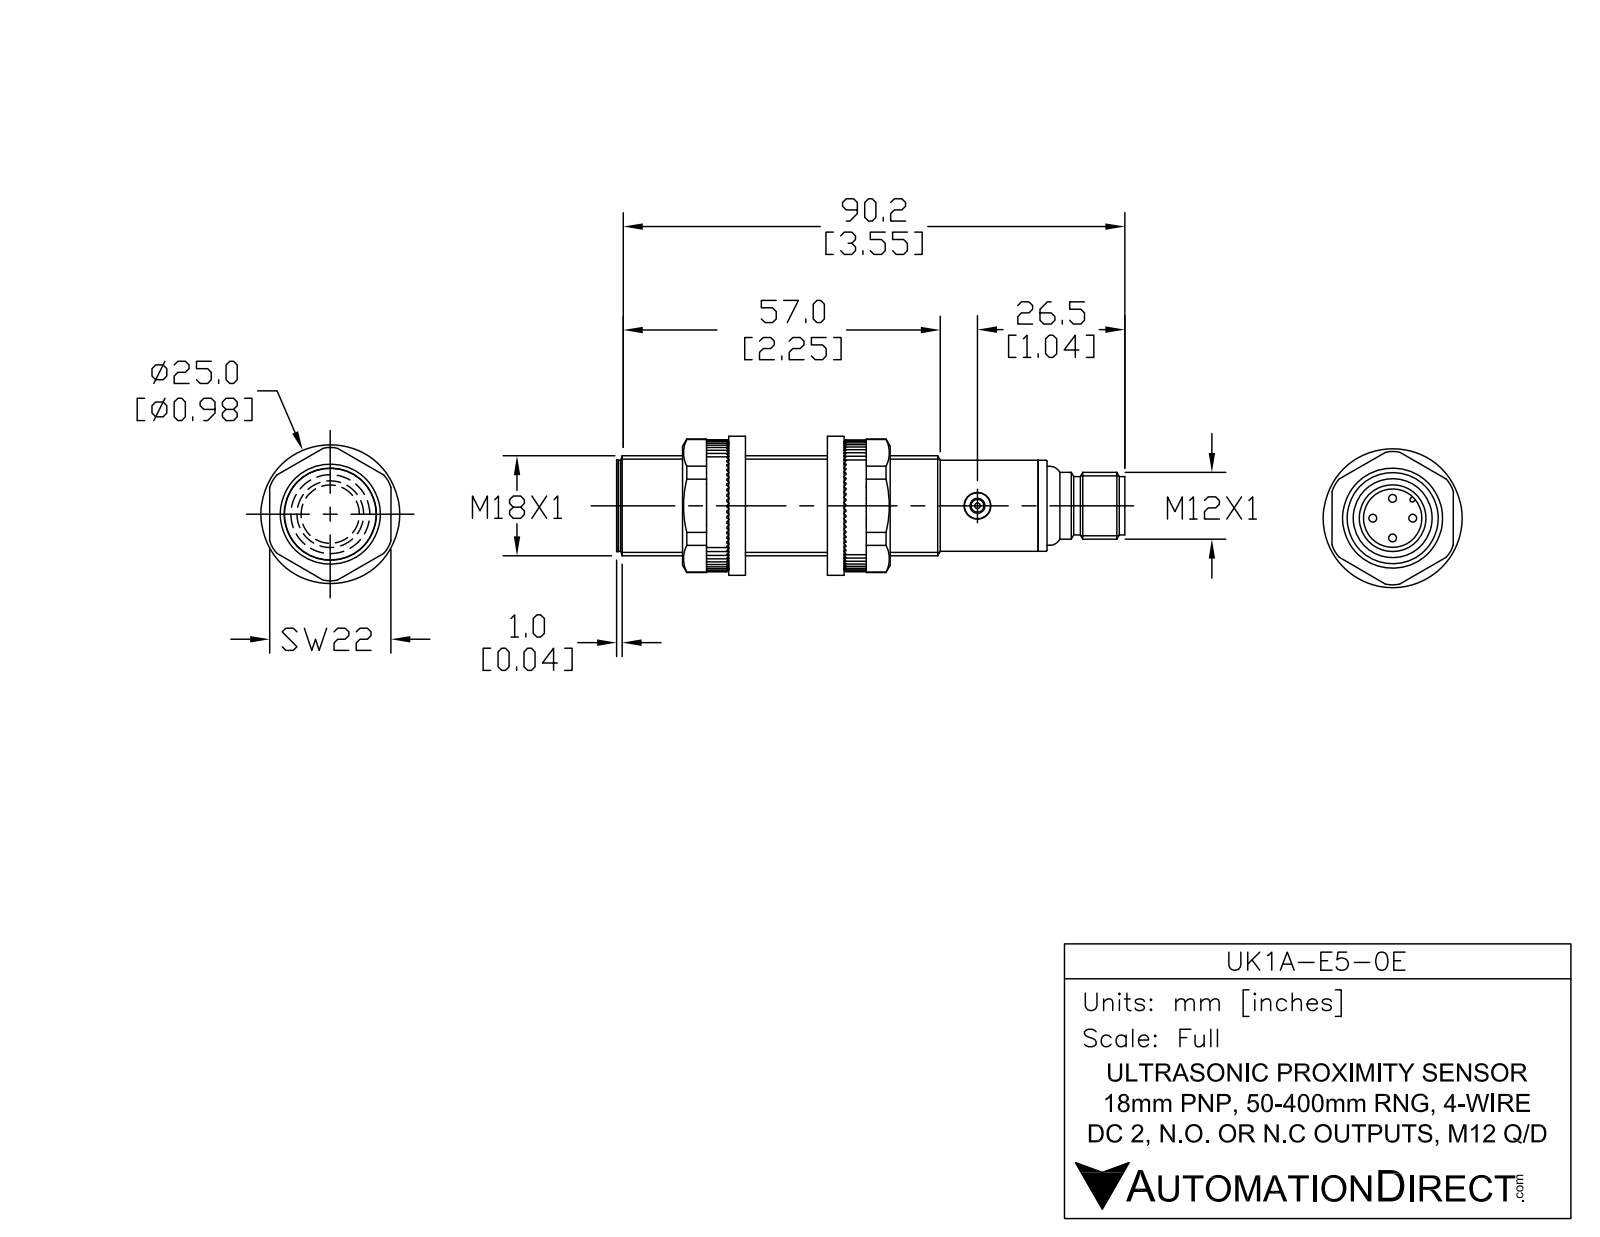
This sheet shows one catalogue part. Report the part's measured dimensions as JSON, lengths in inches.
{"part_name": "UK1A-E5-0E", "step_written_by": "SolidWorks 2017 (AUTOMOTIVE_DESIGN)", "units": "inches", "bodies": {"solids": 6, "faces": 106, "planar": 21, "cylindrical": 48, "other": 37}, "overall_size": [3.606, 0.709, 0.709], "volume_in3": 1.202, "surface_area_in2": 10.68, "round_holes": [[0.106, 1], [0.185, 1], [0.276, 1], [0.327, 1], [0.374, 1]], "round_bosses_or_shafts": [[0.039, 4], [0.709, 1], [0.654, 1], [0.646, 1], [0.622, 1], [0.559, 1], [0.472, 1], [0.413, 1]], "partial_cylinders_radius": [[0.024, 1]], "face_to_face_distances": [2.957, 0.039, 2.996, 0.037, 2.994, 0.043, 0.157, 3.055, 3.053, 3.016]}
